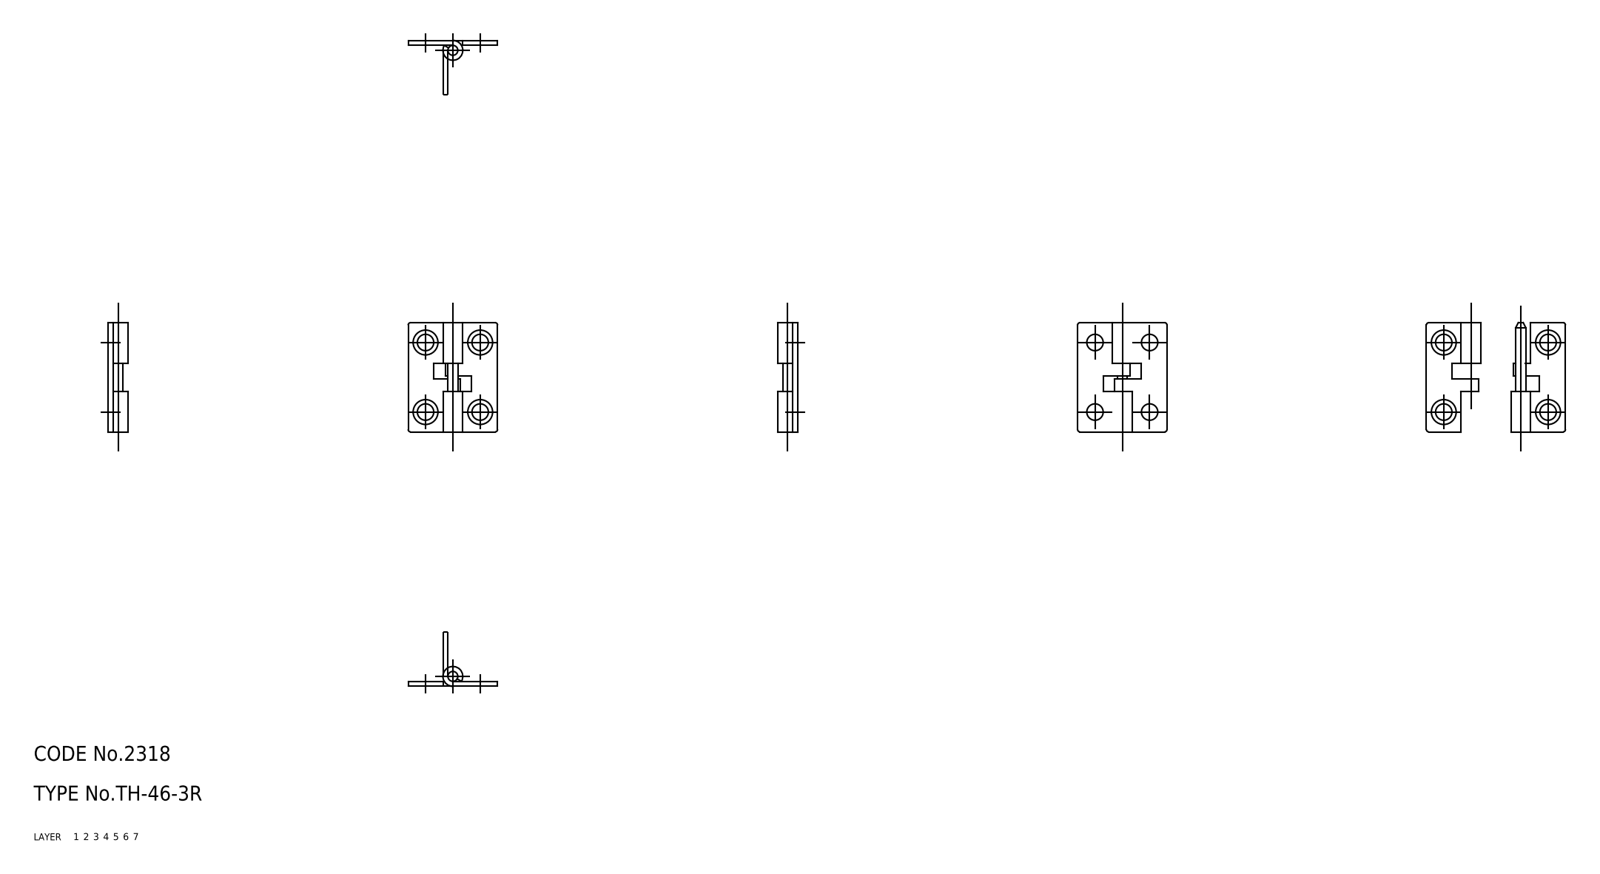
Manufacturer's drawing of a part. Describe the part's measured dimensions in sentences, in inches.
The part is named "shaft; hinge piece_B; hinge piece_A; TH_46_3R_9708_36". Its 3-D file was written by "CADfix (AUTOMOTIVE_DESIGN)". It is 3 solids with 54 faces: 0 planar, 0 cylindrical and 54 other. Overall it measures 0.866 by 0.709 by 0.157 inches. Its volume is 0.03 cubic inches and its surface area 1.896 square inches.
